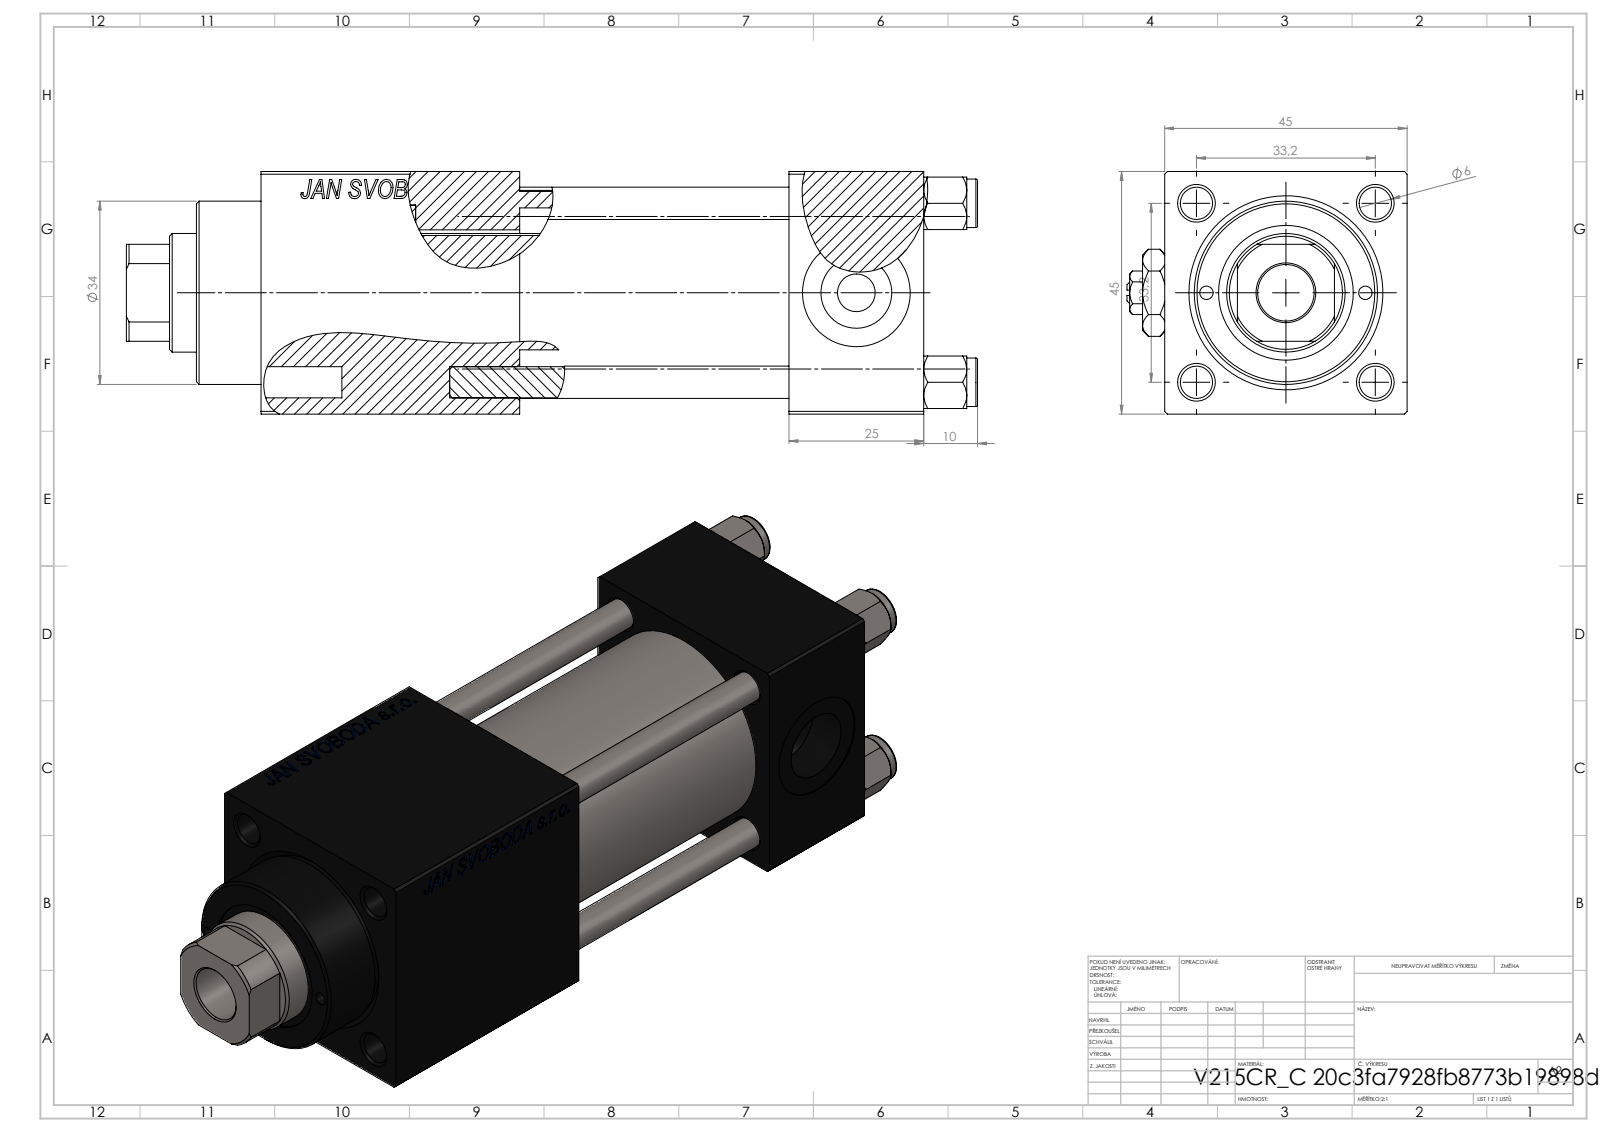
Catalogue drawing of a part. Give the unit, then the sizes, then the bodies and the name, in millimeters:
Units: millimetres
Overall size (bounding box): 158 × 52 × 45
Round holes (diameter × count): ⌀6 ×4, ⌀2.5 ×2, ⌀7 ×2, ⌀13.16 ×2, ⌀20 ×2, ⌀10.5 ×1, ⌀22 ×1, ⌀24 ×1, ⌀25 ×1, ⌀32 ×1, ⌀33 ×1
Round bosses / shafts (diameter × count): ⌀9 ×4, ⌀38 ×1, ⌀34 ×1
Partial cylindrical surfaces — rounded edges, fillets, slot ends (radius × count): R10.5 ×1
Main face-to-face distances: 45, 25, 50, 123, 75, 98, 48, 94.3, 69.3, 19.3
Hole centre spacings: 16.7, 23.48, 33.2, 35.47, 14.75, 46.95, 29.5, 75.5
Volume: 208 843 mm³ · Surface area: 72 648 mm²
Bodies: 12 solids, 1206 faces (550 planar, 98 cylindrical, 558 other)
Part name (STEP PRODUCT): V215_VC_A; V215CR_C_Body; V215CR_VCP_C; Zatka_pro_OIL_PORT (+2 more)
STEP written by: SolidWorks 2019 (CONFIG_CONTROL_DESIGN)
